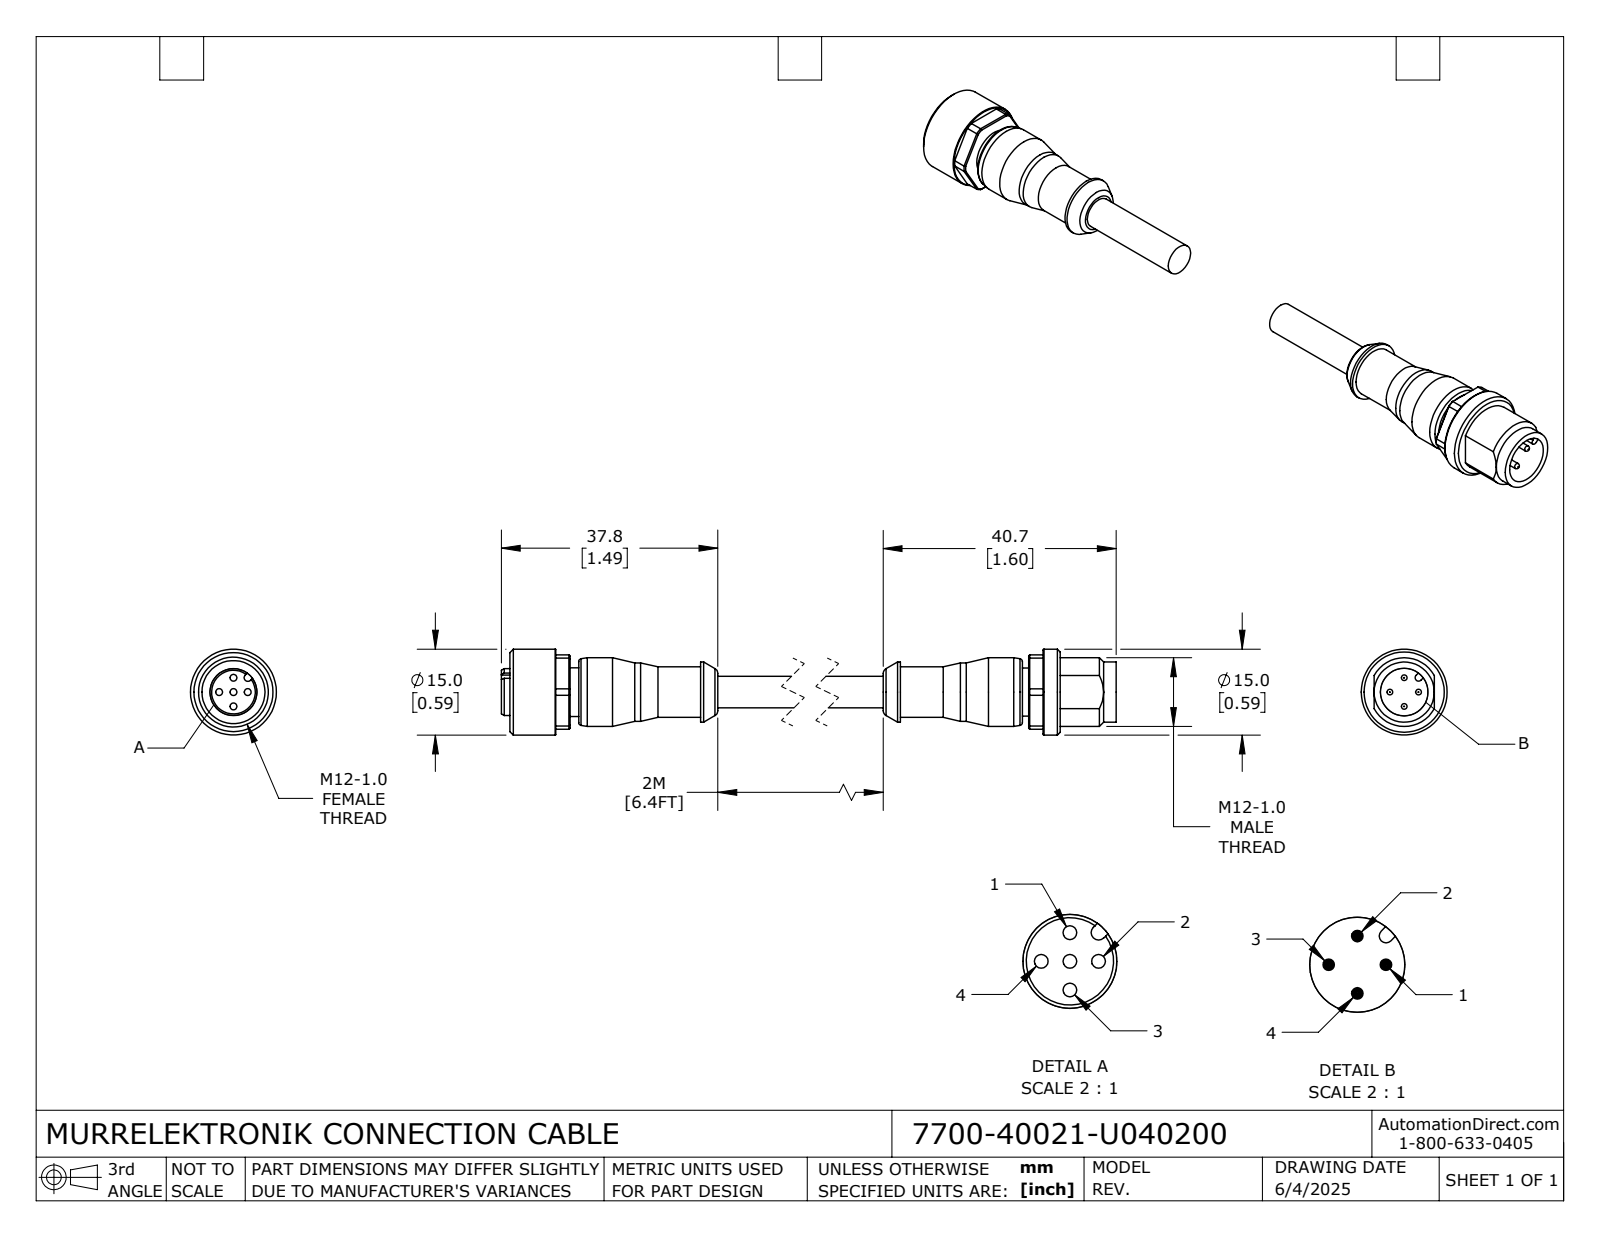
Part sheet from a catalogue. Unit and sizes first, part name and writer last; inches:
Units: inches
Overall size (bounding box): 5.65 × 0.591 × 0.591
Round holes (diameter × count): ⌀0.047 ×5, ⌀0.327 ×1, ⌀0.433 ×1
Round bosses / shafts (diameter × count): ⌀0.039 ×4, ⌀0.591 ×1, ⌀0.472 ×1, ⌀0.413 ×1, ⌀0.402 ×1, ⌀0.346 ×1, ⌀0.335 ×1, ⌀0.331 ×1
Partial cylindrical surfaces — rounded edges, fillets, slot ends (radius × count): R0.024 ×1, R0.026 ×1, R0.283 ×1
Main face-to-face distances: 0.512, 0.118, 4.575, 0.413, 4.945, 0.472, 4.791, 0.295, 0.059, 0.098
Hole centre spacings: 0.098, 0.139, 0.197
Volume: 0.487 in³ · Surface area: 7.972 in²
Bodies: 2 solids, 191 faces (59 planar, 71 cylindrical, 61 other)
Part name (STEP PRODUCT): 7700-40021-U040200_FEMALE; 7700-40021-U040200; 7700-40021-U040200_MALE
STEP written by: SolidWorks 2024 (CONFIG_CONTROL_DESIGN)
